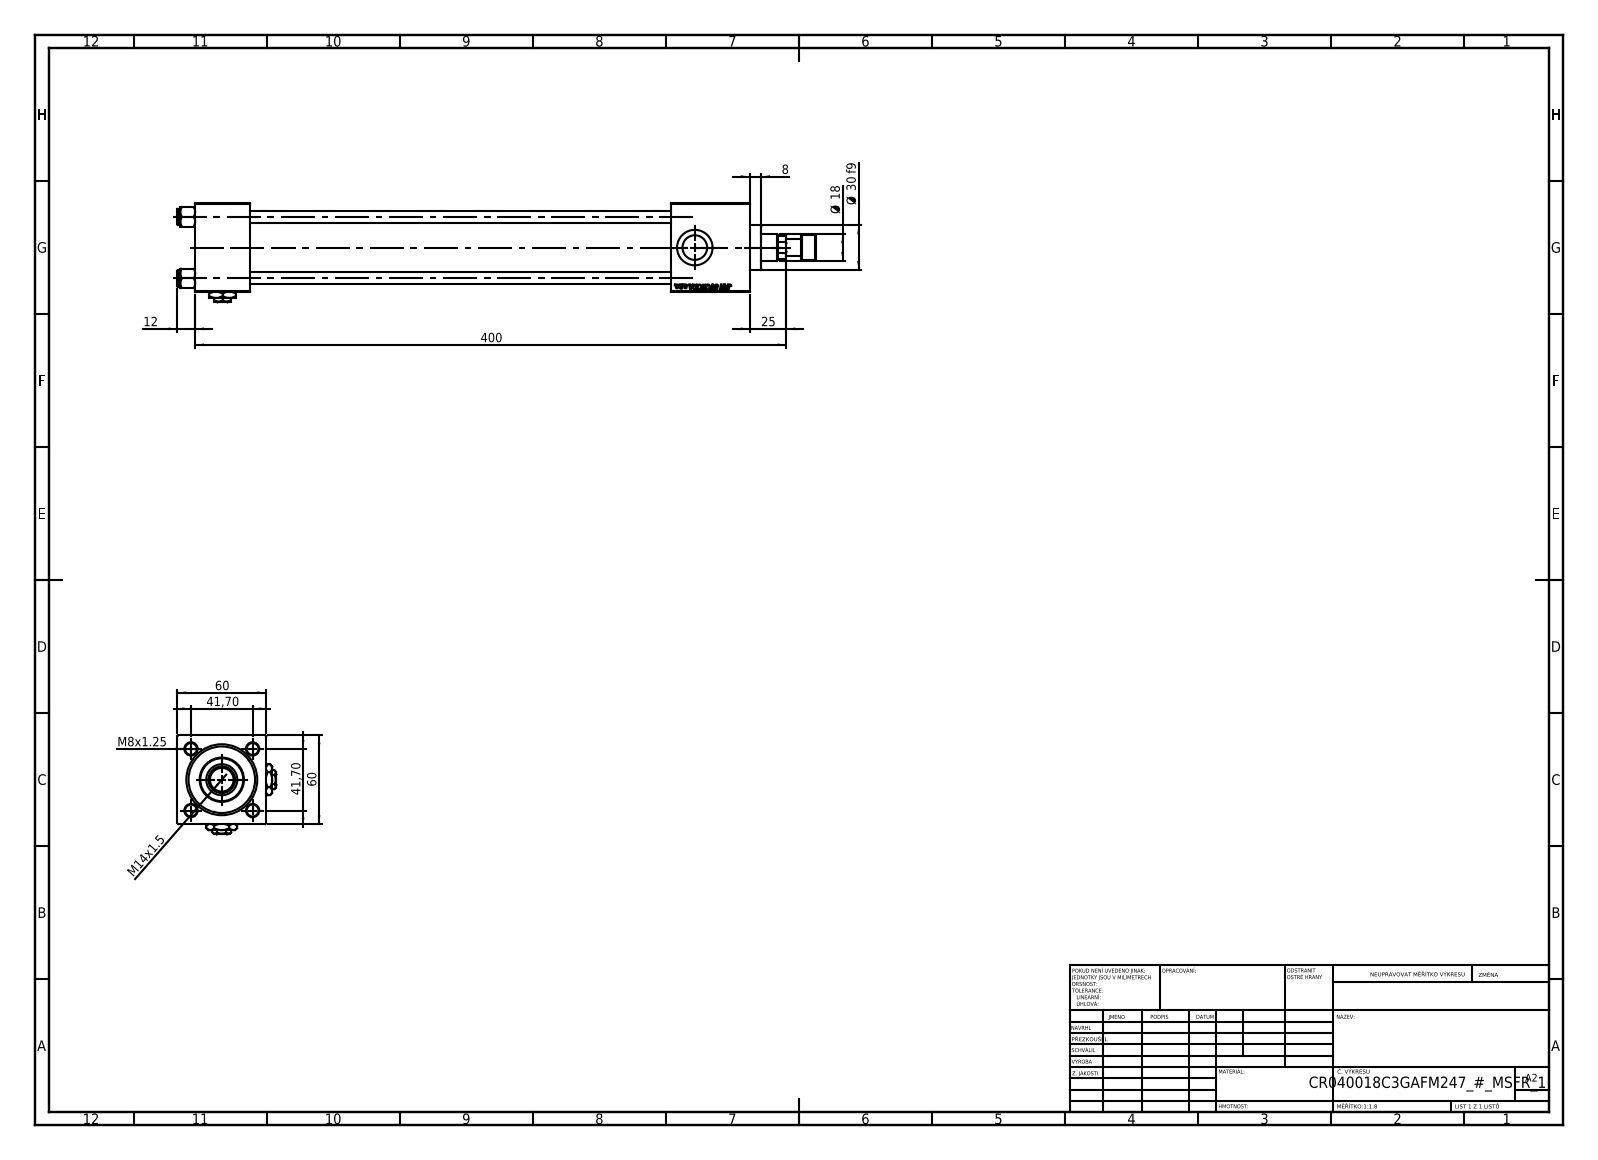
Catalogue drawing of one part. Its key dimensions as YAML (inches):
part_name: "V215_VC_A; V215CR_C_Body; V215CR_C_TYCINKA; NUT_M5_C (+3 more)"
step_written_by: "SolidWorks 2019 (CONFIG_CONTROL_DESIGN)"
units: inches
bodies: {solids: 14, faces: 1261, planar: 577, cylindrical: 102, other: 582}
overall_size: [17.008, 2.638, 2.638]
volume: 36.46
surface_area: 320.3
round_holes:
  - {diameter: 0.315, count: 4}
  - {diameter: 0.276, count: 2}
  - {diameter: 0.656, count: 2}
  - {diameter: 0.945, count: 2}
  - {diameter: 0.335, count: 1}
  - {diameter: 0.709, count: 1}
  - {diameter: 0.827, count: 1}
  - {diameter: 1.22, count: 1}
  - {diameter: 1.575, count: 1}
  - {diameter: 1.772, count: 1}
round_bosses_or_shafts:
  - {diameter: 0.433, count: 5}
  - {diameter: 1.811, count: 1}
  - {diameter: 1.181, count: 1}
  - {diameter: 0.669, count: 1}
face_to_face_distances: [2.362, 1.457, 14.764, 13.307, 2.087, 12.677, 11.22, 13.634, 12.177, 0.957]
hole_center_spacings: [1.161, 1.642, 2.322]
